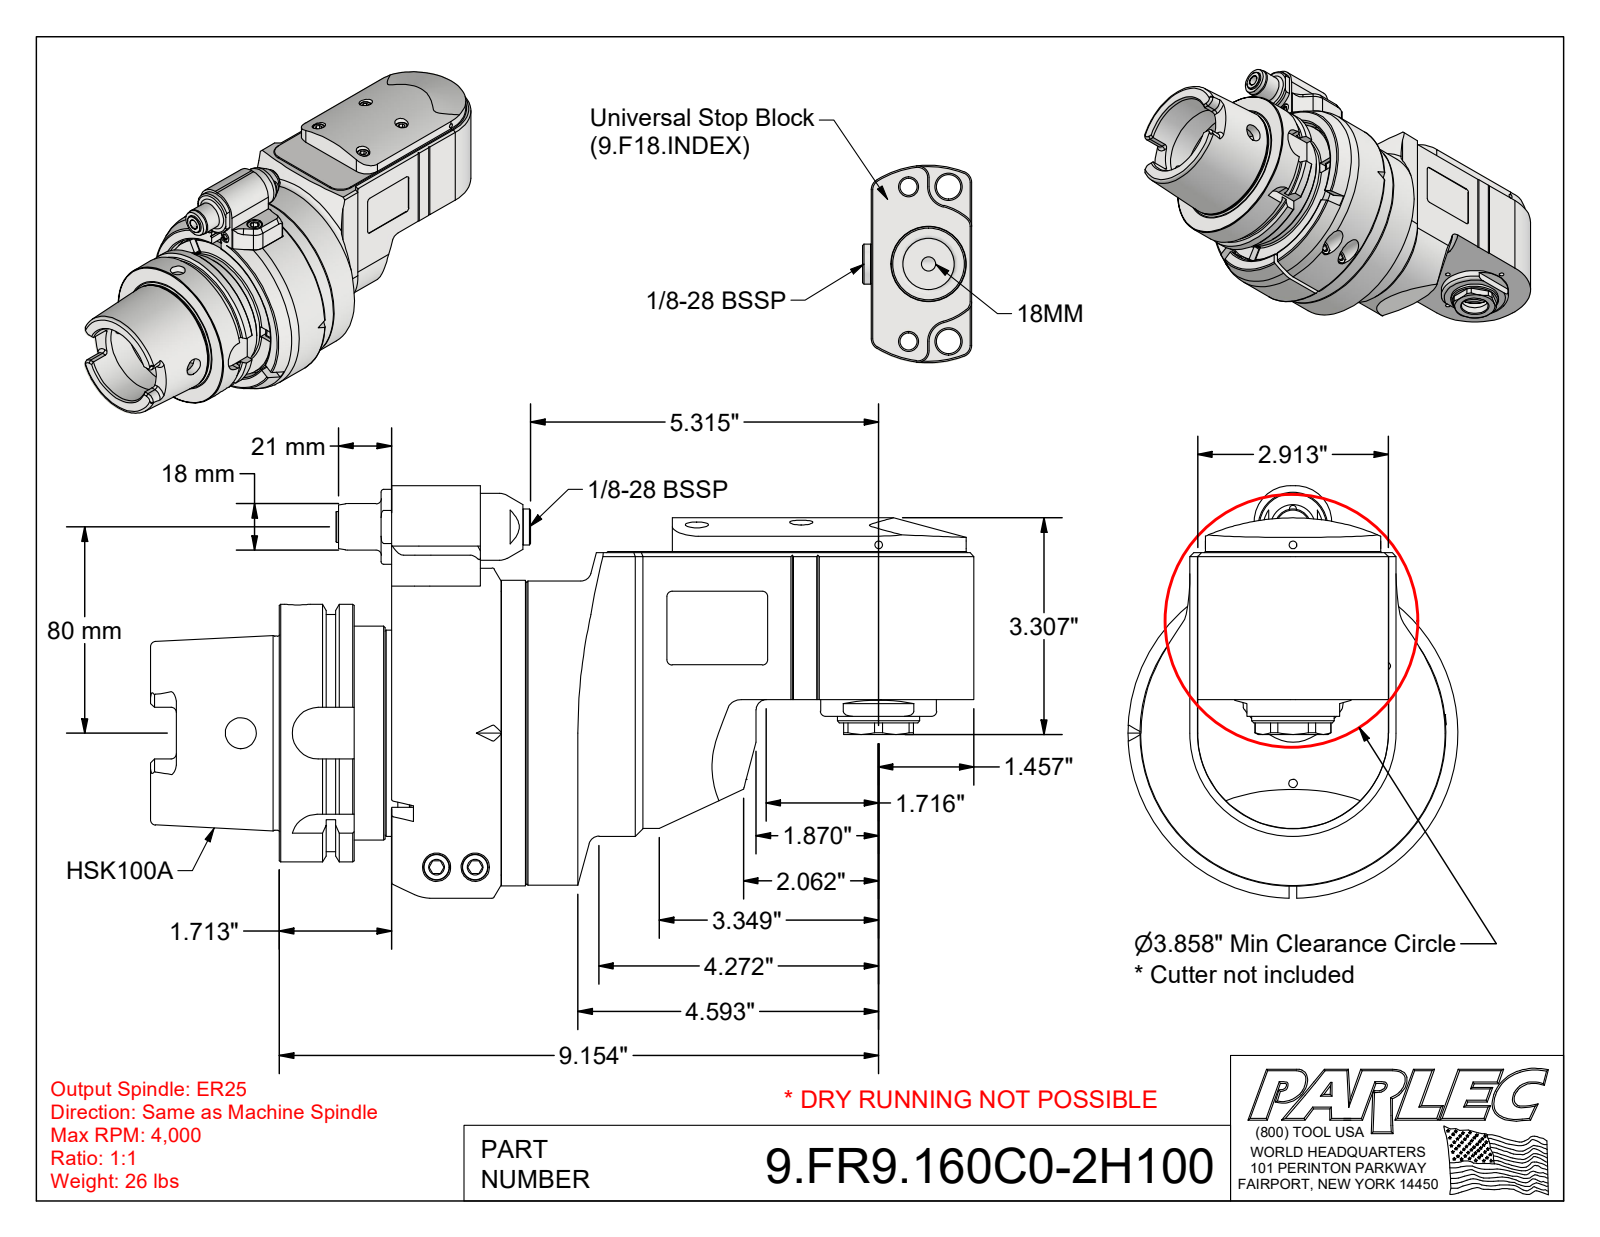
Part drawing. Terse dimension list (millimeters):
name: 9.FR9.160C0-2H100; 9GA21C_518 (Type 2, HSK100 , 80mm); 9_FR9_160B0
written by: Autodesk Inventor 2022 (AUTOMOTIVE_DESIGN)
unit: mm
bodies: 9 solids, 840 faces (382 planar, 240 cylindrical, 218 other)
size: 319.5 × 160 × 128
volume: 2 065 000 mm³; area: 255 500 mm²
holes: 20× ⌀10.5, 9× ⌀5, 8× ⌀3.2, 4× ⌀9, 3× ⌀3, 3× ⌀3.3, 3× ⌀6.5, 2× ⌀2.6, 2× ⌀4.2, 2× ⌀6, 2× ⌀8, 2× ⌀10.4
bosses: 4× ⌀10, 4× ⌀8.5, 2× ⌀18, 2× ⌀12, 2× ⌀8, 2× ⌀6, 2× ⌀2.5, 1× ⌀128
rounds: 18× R2, 14× R1, 6× R3, 6× R10, 5× R4, 4× R4.9, 2× R0.5, 2× R8
face distances: 35.5, 35, 1, 0.5, 34, 38.5, 74, 7, 52, 3
hole spacings: 46.8, 66.1, 92.6, 34.7, 56.3, 59.6, 11, 34
